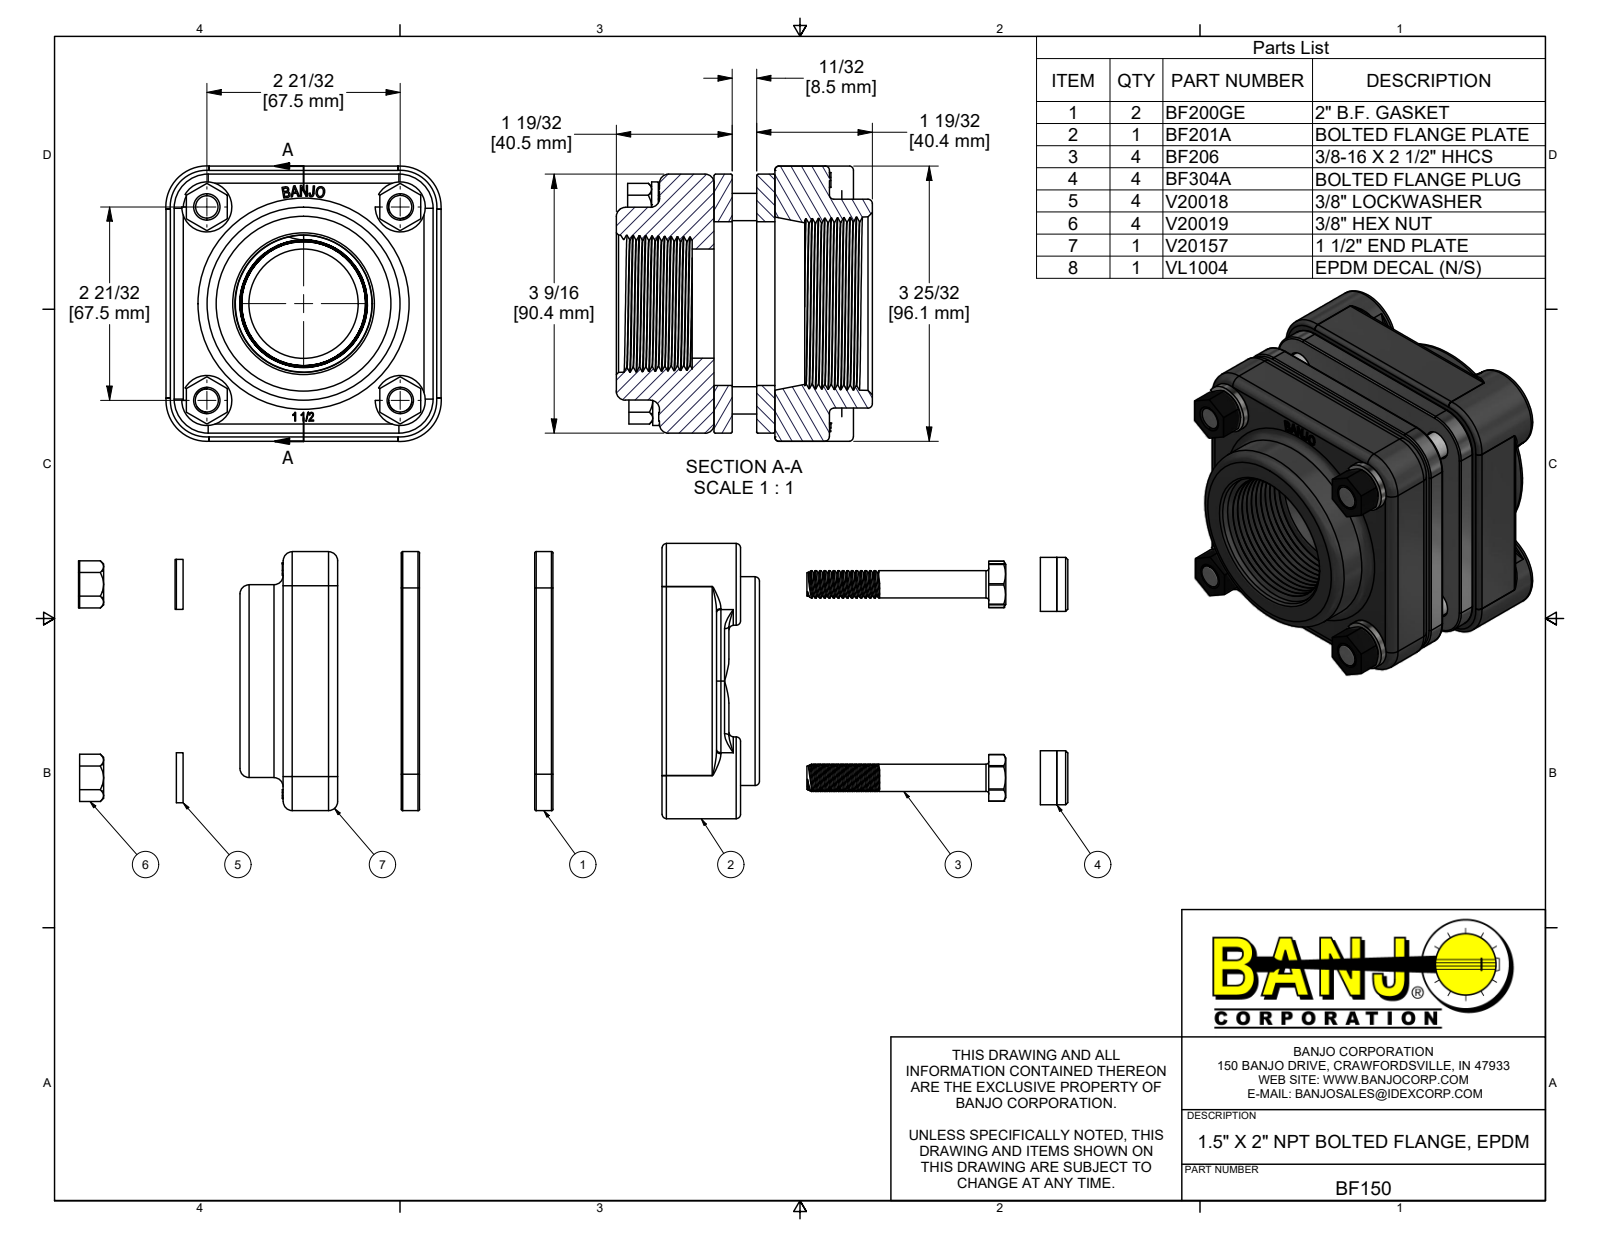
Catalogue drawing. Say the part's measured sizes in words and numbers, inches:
The part is named "BF150; V20157; BF200GE; BF206 (+4 more)". Its 3-D file was written by "Autodesk Inventor 2019 (AUTOMOTIVE_DESIGN)". It is 20 solids with 1228 faces: 378 planar, 346 cylindrical and 504 other. Overall it measures 30.375 by 3.784 by 3.784 inches. Its volume is 24.12 cubic inches and its surface area 359.3 square inches. Round holes: 4 of diameter 0.307, 4 of diameter 0.38, 4 of diameter 0.385, 4 of diameter 0.406, 4 of diameter 0.41, 4 of diameter 0.715, 4 of diameter 0.75, 1 of diameter 1.5, 1 of diameter 2.25. Round bosses or shafts: 60 of diameter 0.324, 4 of diameter 1.125, 4 of diameter 0.742, 4 of diameter 0.687, 4 of diameter 0.375, 1 of diameter 2.87, 1 of diameter 2.65. Partial cylindrical surfaces (rounded edges, fillets, slot ends): 16 of radius 0.02, 16 of radius 0.06, 8 of radius 0.125, 8 of radius 0.162, 4 of radius 0.32, 4 of radius 0.469, 4 of radius 0.5, 4 of radius 1.6. The main face-to-face distances are 0.835, 0.25, 0.585, 0.335, 0.111, 3.671, 0.75, 1, 1.335, 1.585. The hole center spacings are 1.88, 2.659, 3.761.
